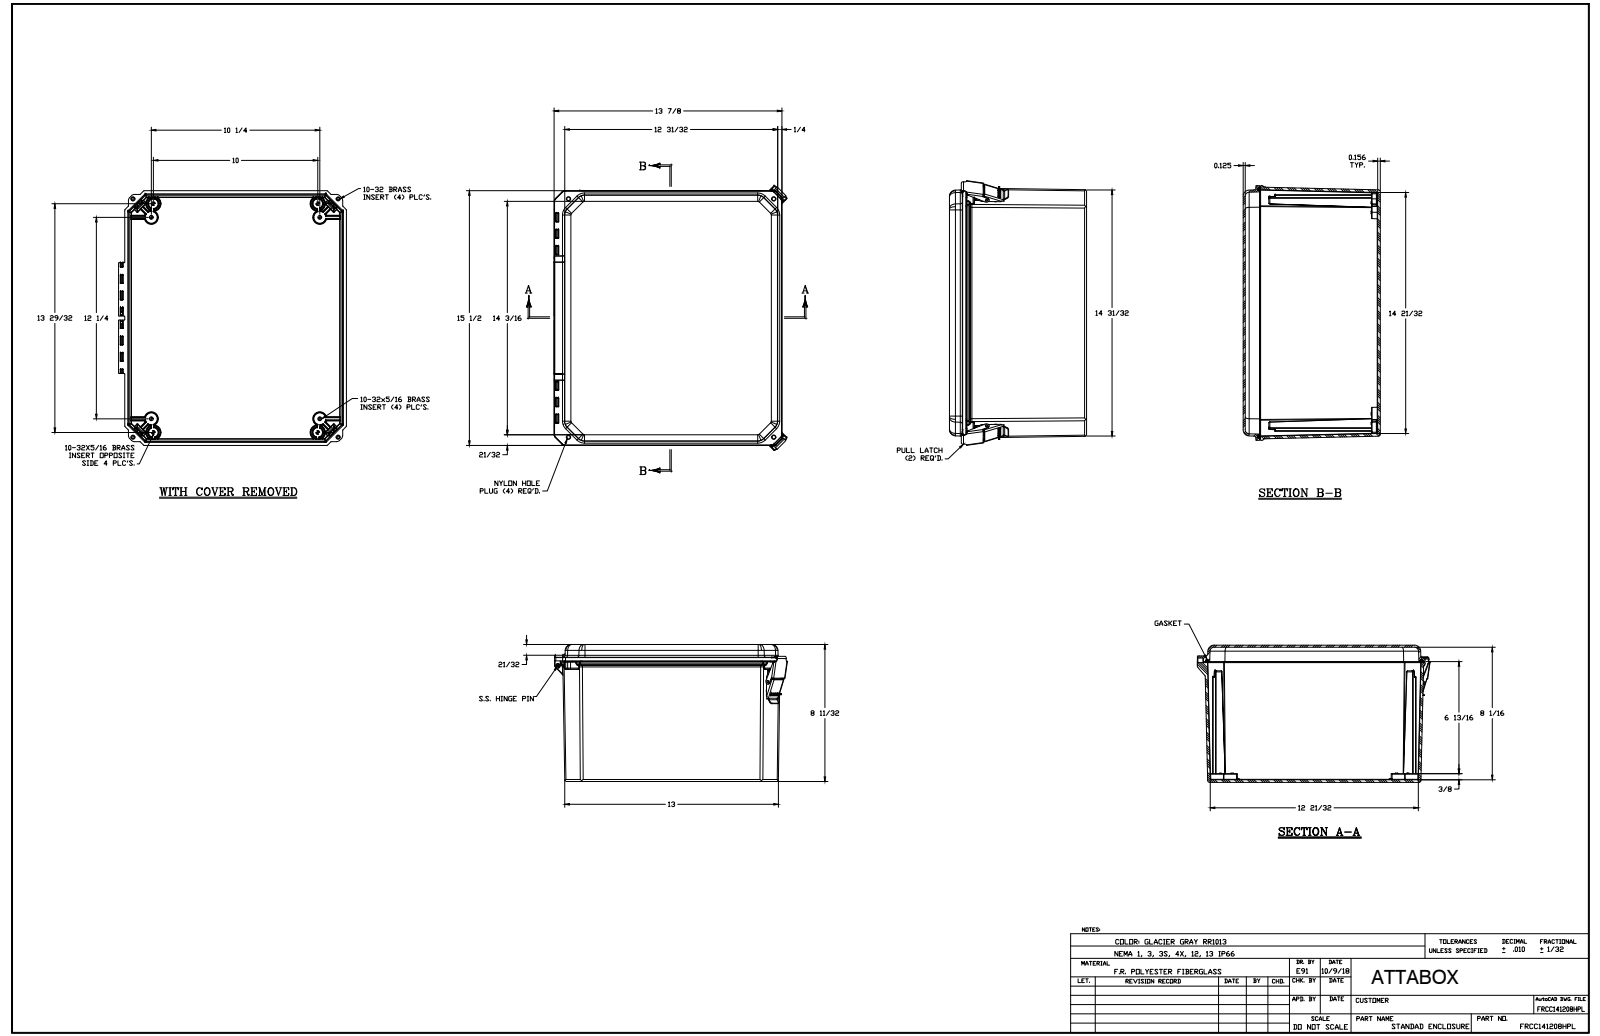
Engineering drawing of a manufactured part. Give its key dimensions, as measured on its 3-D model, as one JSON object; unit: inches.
{"part_name": "FRCC141208HPL", "step_written_by": "SolidWorks 2018 (AUTOMOTIVE_DESIGN)", "units": "inches", "bodies": {"solids": 29, "faces": 2318, "planar": 713, "cylindrical": 924, "other": 681}, "overall_size": [16.2, 14.223, 8.343], "volume_in3": 134.2, "surface_area_in2": 1813, "round_holes": [[0.156, 12], [0.152, 8], [0.135, 6], [0.135, 4], [0.15, 4], [0.219, 4], [0.252, 4], [0.312, 4], [0.375, 2], [0.137, 1]], "round_bosses_or_shafts": [[0.246, 12], [0.209, 4], [0.3, 2], [0.135, 1]], "partial_cylinders_radius": [[0.01, 202], [0.005, 116], [0.02, 59], [0.03, 58], [0.125, 29], [0.09, 26], [0.03, 24], [0.06, 24]], "face_to_face_distances": [0.125, 0.156, 8.218, 8.062, 8.343, 8.187, 0.16, 0.159, 1, 7.343], "hole_center_spacings": [0.25, 1.584, 17.55, 18.104, 0.828, 1.281, 10.158, 11.249]}
